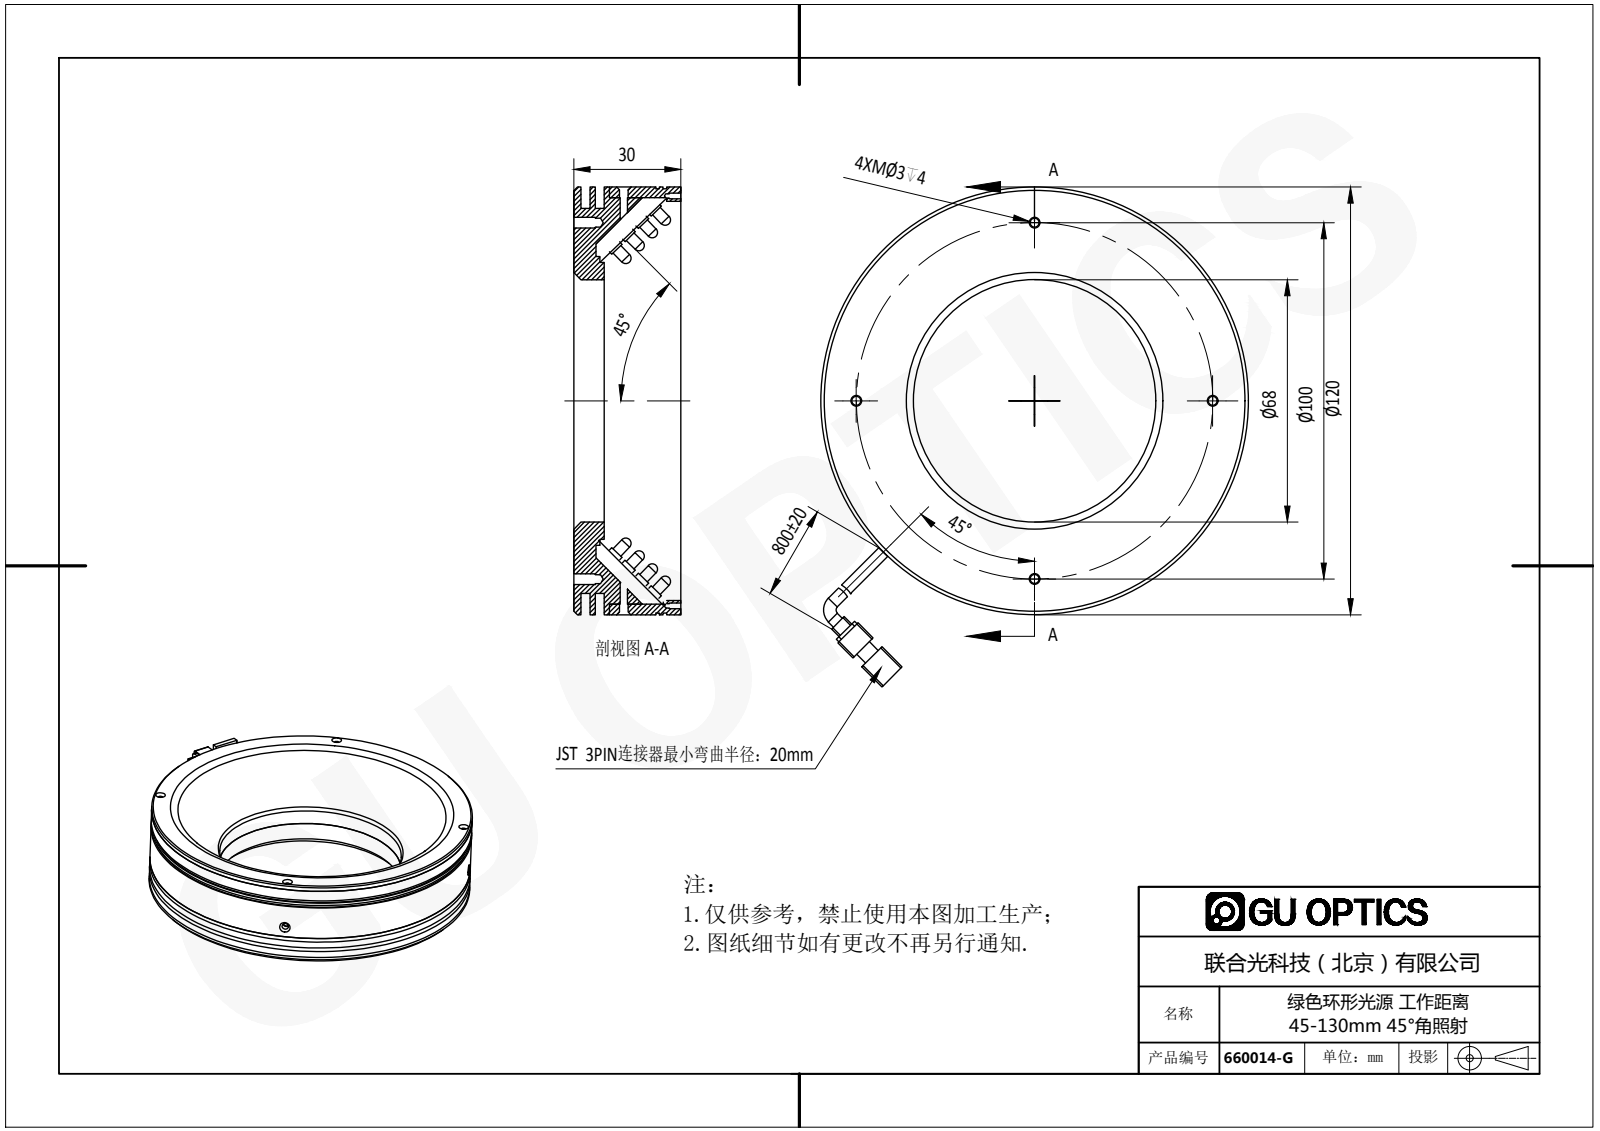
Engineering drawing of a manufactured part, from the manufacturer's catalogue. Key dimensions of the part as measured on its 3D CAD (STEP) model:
Part name (STEP PRODUCT): 660014-G
STEP written by: SolidWorks 2016 (AUTOMOTIVE_DESIGN)
Units: millimetres
Bodies: 266 solids, 4721 faces (3214 planar, 1182 cylindrical, 325 other)
Overall size (bounding box): 140.26 × 120 × 32
Volume: 128 993 mm³ · Surface area: 114 112 mm²
Round holes (diameter × count): ⌀1.2 ×4, ⌀1.6 ×4, ⌀1.7 ×4, ⌀2.5 ×4, ⌀3 ×4, ⌀3.5 ×4, ⌀2 ×2, ⌀2.4 ×2, ⌀68 ×1, ⌀112 ×1
Round bosses / shafts (diameter × count): ⌀3.8 ×260, ⌀3 ×260, ⌀3.5 ×2, ⌀120 ×1, ⌀119 ×1, ⌀114 ×1, ⌀108 ×1, ⌀81 ×1
Partial cylindrical surfaces — rounded edges, fillets, slot ends (radius × count): R0.5 ×8, R1 ×4, R1.6 ×1, R6 ×1
Main face-to-face distances: 4, 30, 2, 2.5, 1.5, 21.5, 8.5, 6, 24, 20
Hole centre spacings: 76.2, 7.5, 50, 57.5, 70.71, 81.32, 107.5, 100
